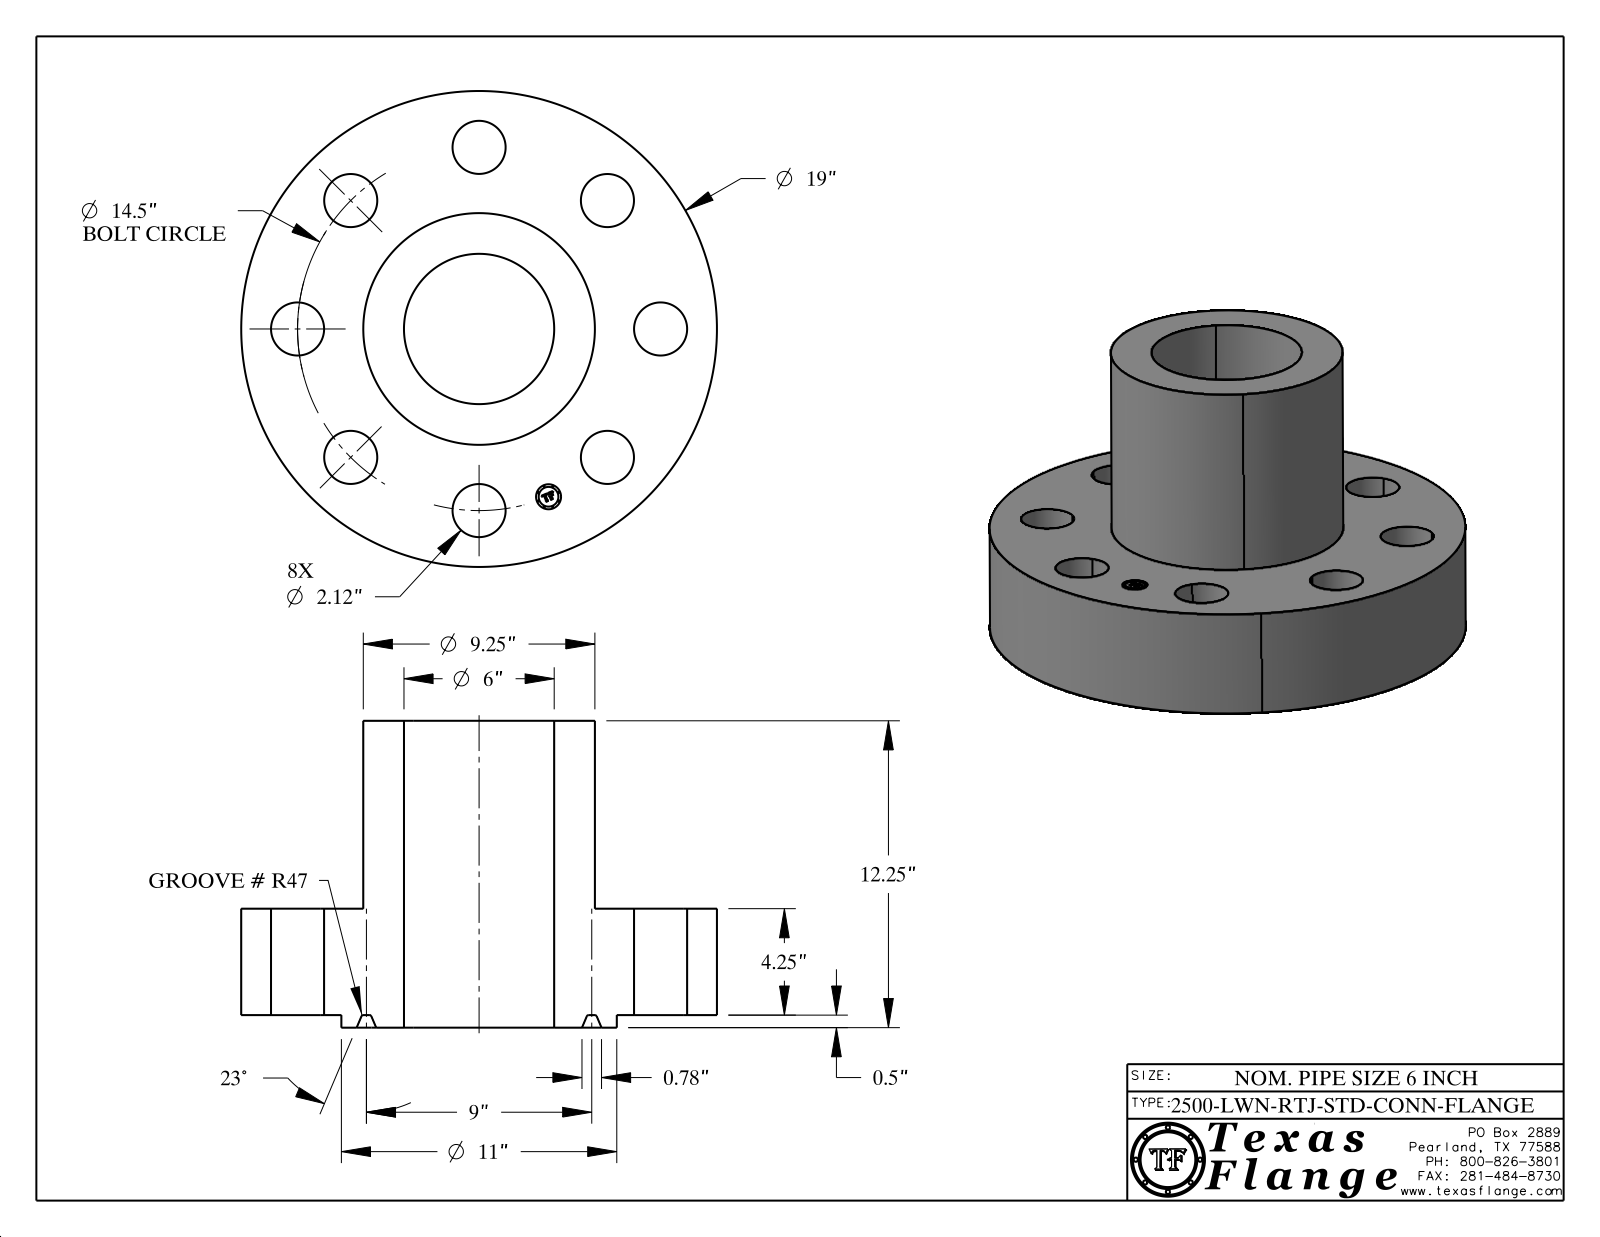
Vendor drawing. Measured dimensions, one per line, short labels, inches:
name: 6-2500-LWN-RTJ-STD-CONN-FLANGE
written by: CATIA V5 STEP AP214 (AUTOMOTIVE_DESIGN)
unit: in
bodies: 1 solid, 423 faces (371 planar, 44 cylindrical, 8 other)
size: 19 × 19 × 12.25
volume: 1 282 in³; area: 1 419 in²
holes: 8× ⌀2.12, 1× ⌀1, 1× ⌀6
bosses: 8× ⌀0.061, 1× ⌀19, 1× ⌀11, 1× ⌀9.25, 1× ⌀0.788
face distances: 4.25, 0.5, 4.75, 12.25, 11.75, 7.5, 4.745, 4.245, 7.505, 0.298
hole spacings: 5.549, 13.396, 7.25, 7.25, 10.253, 10.253, 2.829, 14.221
